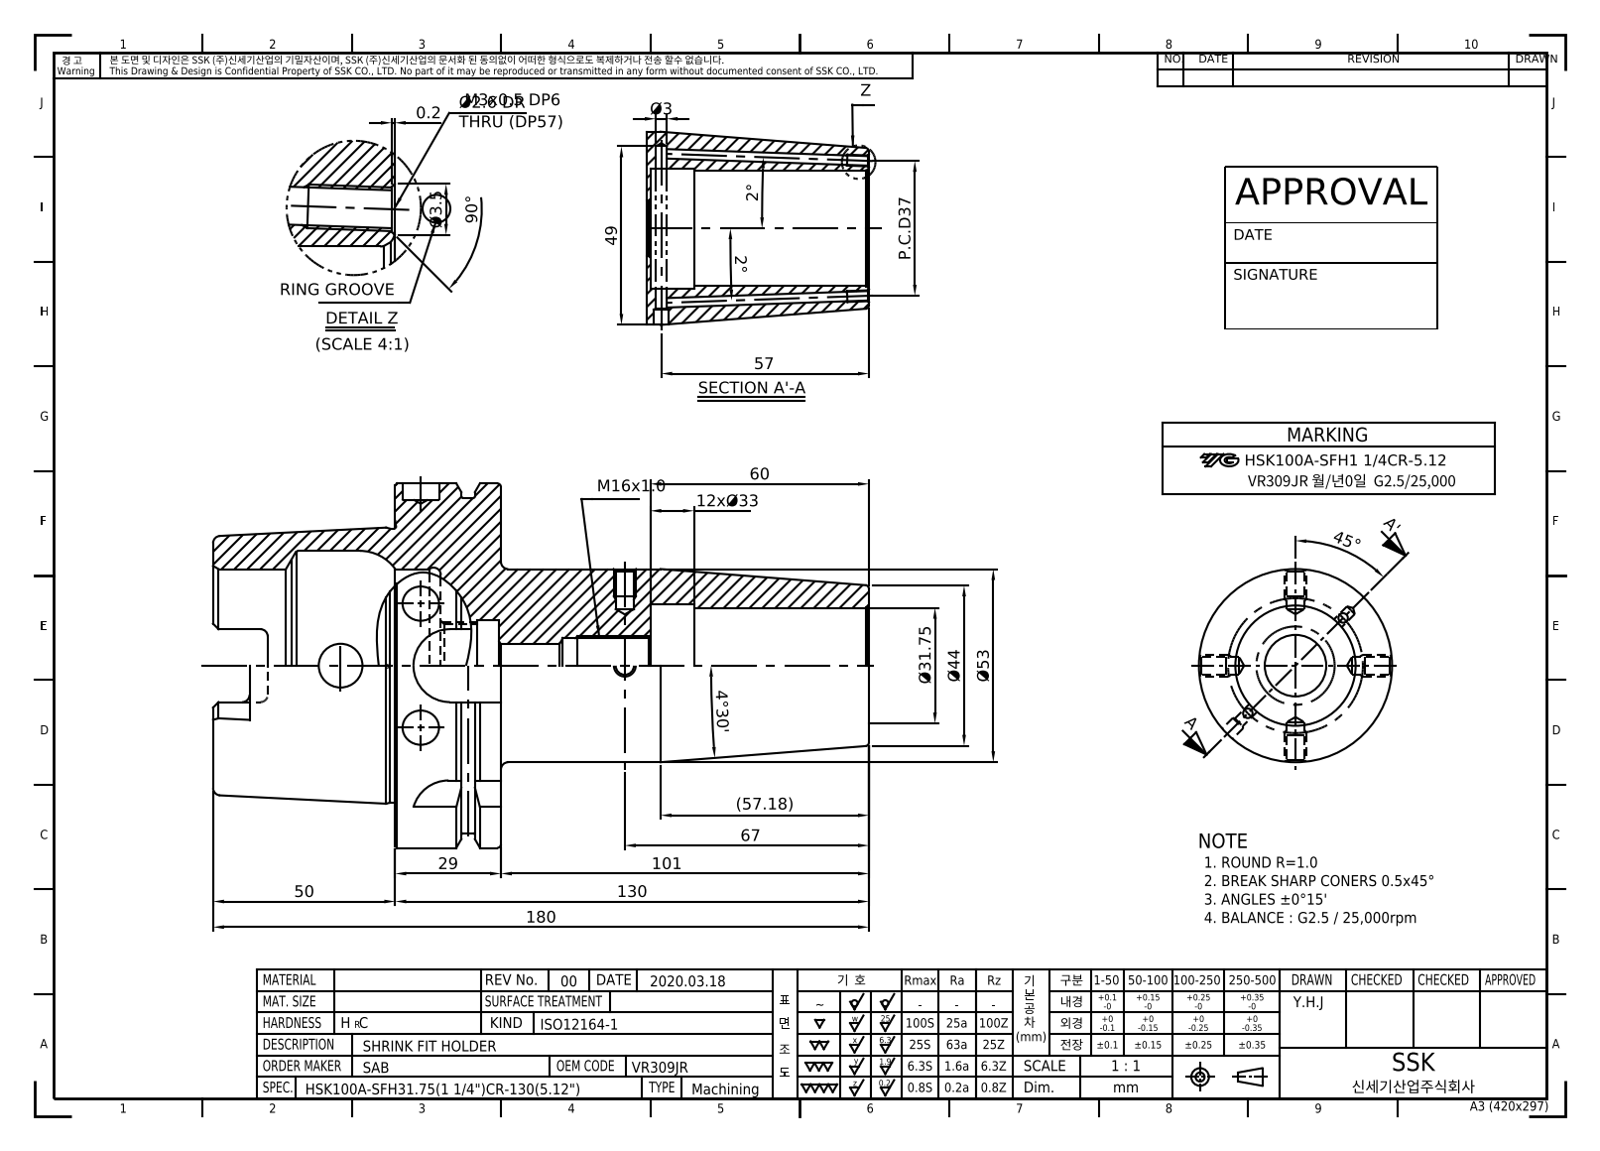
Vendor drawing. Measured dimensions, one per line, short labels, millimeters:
name: LO-HSK100A-SFH31.75CR-130
written by: Autodesk Inventor 2022 (AUTOMOTIVE_DESIGN)
unit: mm
bodies: 1 solid, 119 faces (38 planar, 37 cylindrical, 44 other)
size: 180 × 100 × 100
volume: 402 723 mm³; area: 73 212 mm²
holes: 2× ⌀2.46, 2× ⌀12, 1× ⌀10, 1× ⌀14.92, 1× ⌀22.38, 1× ⌀25, 1× ⌀31.75, 1× ⌀32.95, 1× ⌀53, 1× ⌀63
bosses: 1× ⌀100, 1× ⌀92, 1× ⌀75.41
rounds: 6× R2, 4× R4.88, 4× R10
face distances: 29, 12.5, 16.5, 62.5, 50, 79, 57.5, 120, 70, 41
